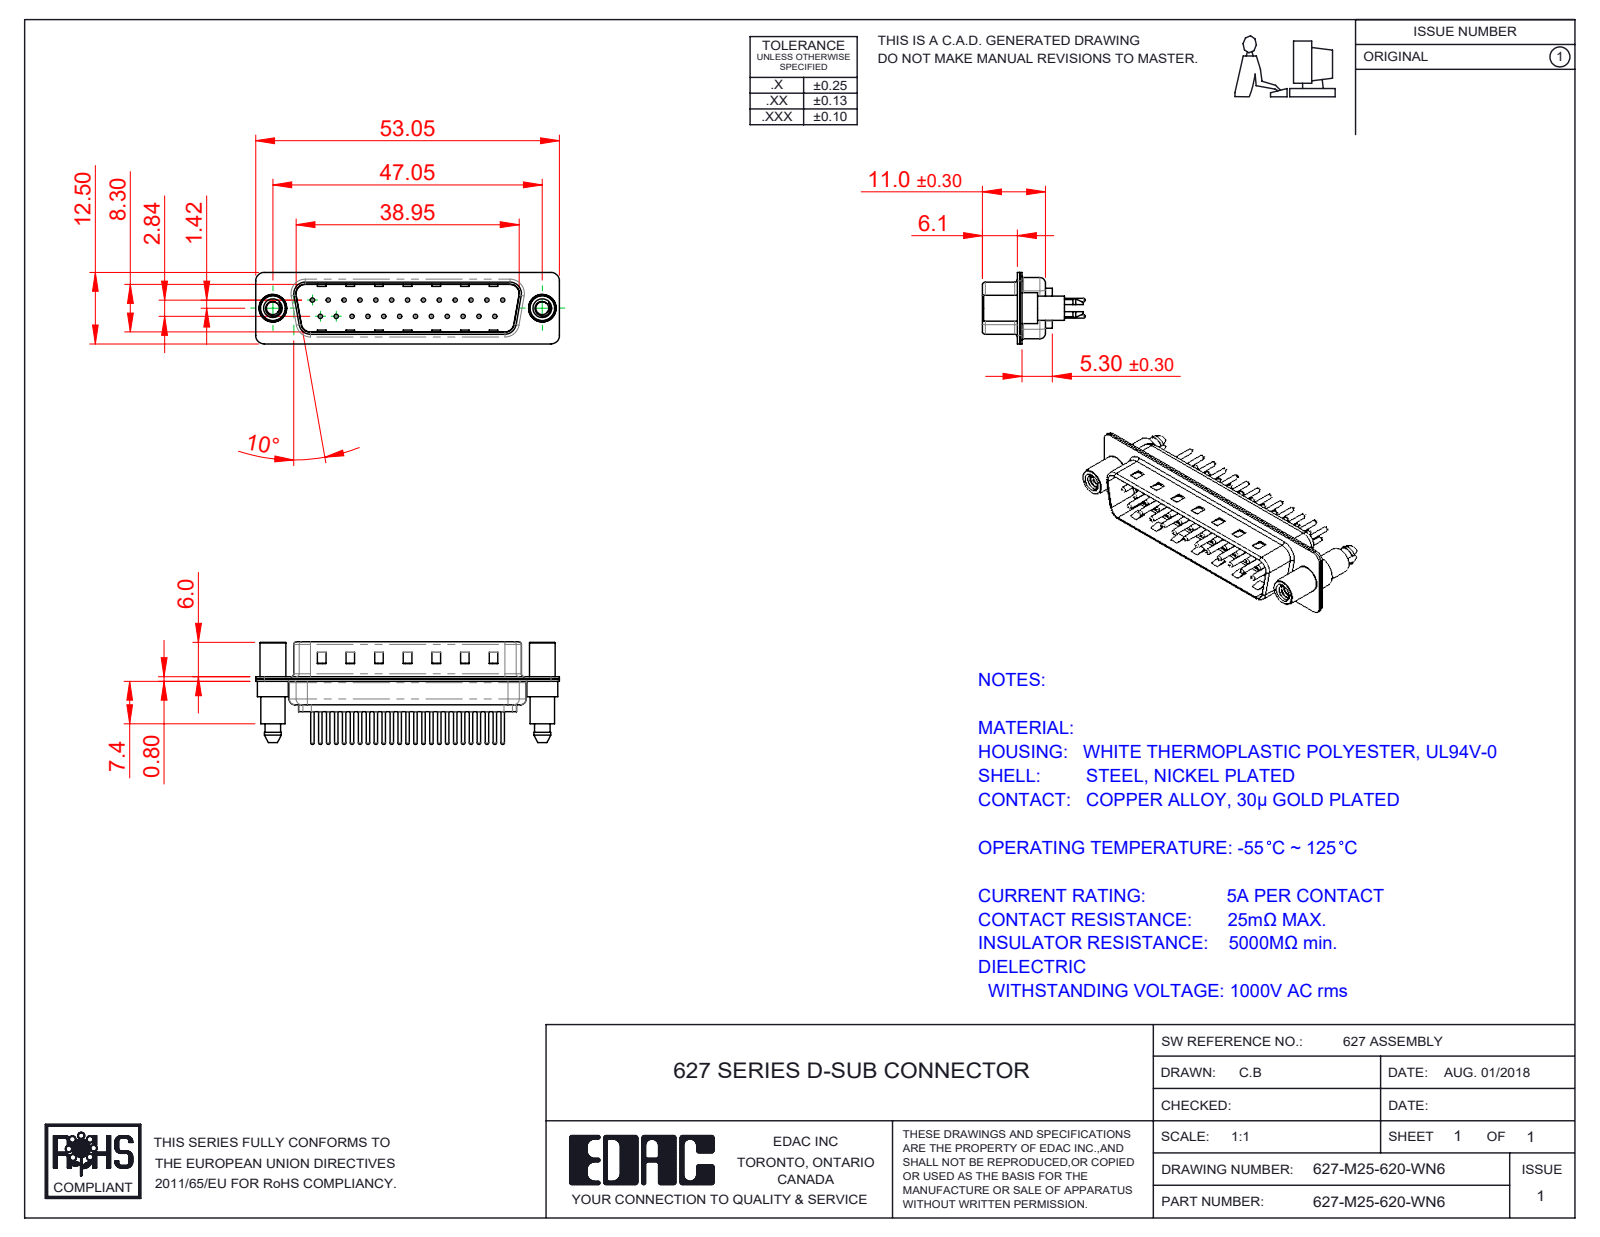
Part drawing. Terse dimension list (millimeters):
name: 627M Contact Row 1_20; 627M 4-40 Threaded Standoff and Boardlock; 627M Contact Row 2_20; 627M Shell Rear_25 Contacts (+3 more)
written by: SolidWorks 2020 (CONFIG_CONTROL_DESIGN)
unit: mm
bodies: 30 solids, 1353 faces (364 planar, 515 cylindrical, 474 other)
size: 53.05 × 17.9 × 12.5
volume: 3 058 mm³; area: 7 311 mm²
holes: 25× ⌀0.75, 25× ⌀1.6, 25× ⌀2, 2× ⌀2.26, 2× ⌀4, 2× ⌀4.8
bosses: 25× ⌀1.5, 25× ⌀0.6, 2× ⌀5.4, 2× ⌀4.9, 2× ⌀4.5, 2× ⌀4.25
rounds: 18× R1.5, 12× R2, 10× R1.6, 8× R0.5, 4× R0.25, 4× R0.6, 4× R0.65, 4× R0.9
face distances: 0.4, 0.8, 9.5, 9.1, 8.7, 9.9, 1.2, 5.7, 6.1, 0.75
hole spacings: 3.16, 2.77, 5.54, 8.31, 11.08, 13.85, 16.62, 5.03
